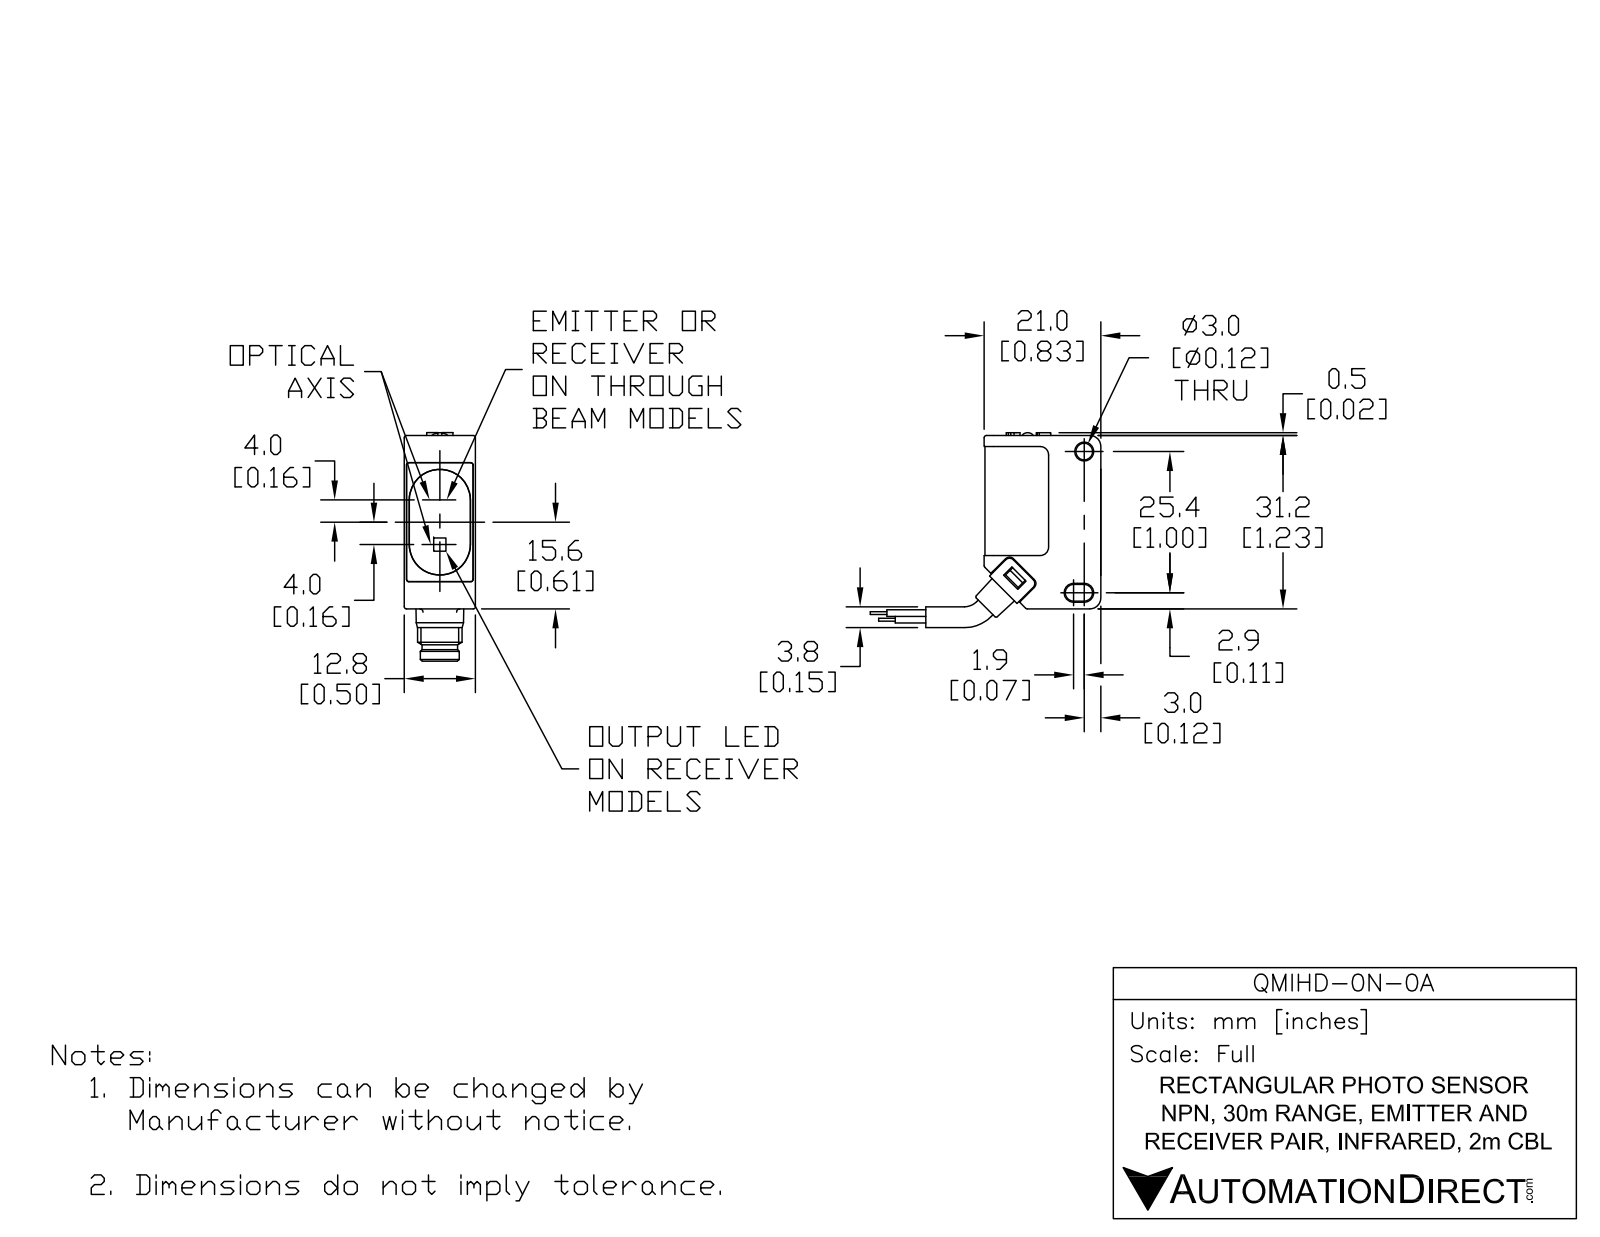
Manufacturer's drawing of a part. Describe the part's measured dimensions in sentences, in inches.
The part is named "QMIHD-0N-0A". Its 3-D file was written by "SolidWorks 2017 (AUTOMOTIVE_DESIGN)". It is 8 solids with 236 faces: 123 planar, 89 cylindrical and 24 other. Overall it measures 3.181 by 1.02 by 0.512 inches. Its volume is 0.47 cubic inches and its surface area 8.336 square inches. Round holes: 2 of diameter 0.118, 1 of diameter 0.148, 1 of diameter 0.224, 1 of diameter 0.283. Round bosses or shafts: 1 of diameter 0.138. Partial cylindrical surfaces (rounded edges, fillets, slot ends): 13 of radius 0.016, 8 of radius 0.039, 6 of radius 0.02, 6 of radius 0.059, 4 of radius 0.024, 2 of radius 0.035, 2 of radius 0.065, 2 of radius 0.079. The main face-to-face distances are 0.02, 0.498, 0.016, 0.504, 0.059, 0.138, 0.488, 0.079, 0.482, 0.492.
